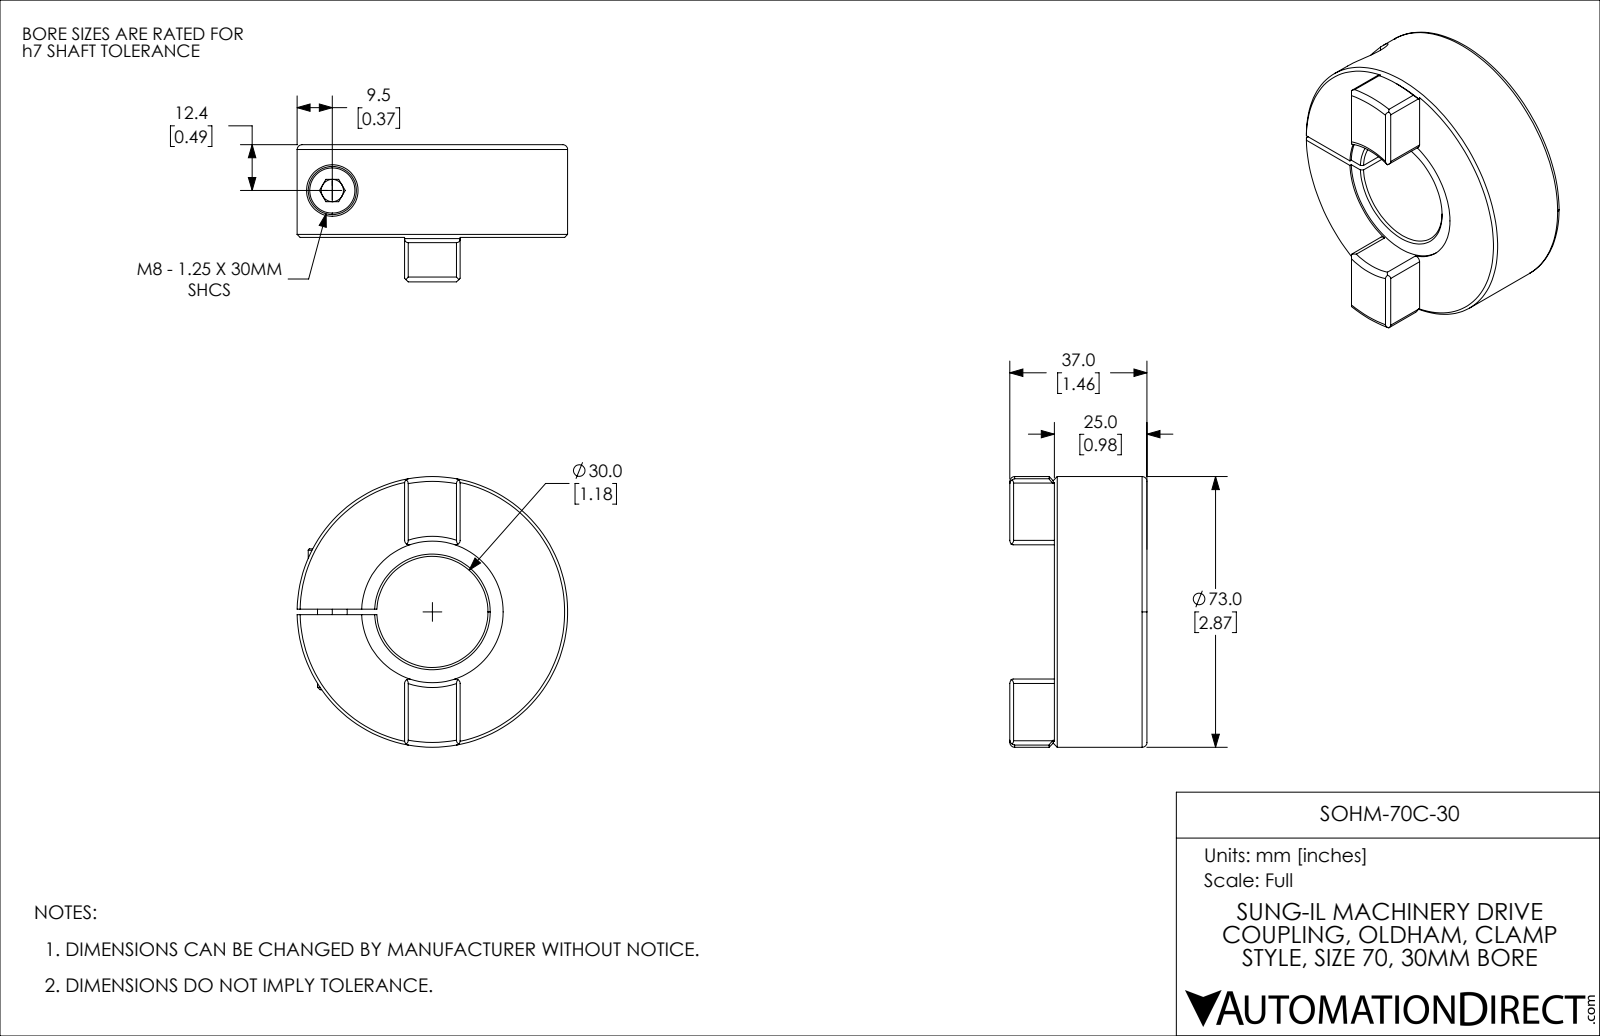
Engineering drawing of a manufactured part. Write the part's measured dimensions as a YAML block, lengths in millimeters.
part_name: "SOHM-70C-30"
step_written_by: "SolidWorks 2021 (CONFIG_CONTROL_DESIGN)"
units: millimeters
bodies: {solids: 2, faces: 90, planar: 35, cylindrical: 30, other: 25}
overall_size: [73, 72.99, 37]
volume: 90678
surface_area: 19754
round_holes:
  - {diameter: 6, count: 1}
  - {diameter: 6.8, count: 1}
  - {diameter: 8.5, count: 1}
  - {diameter: 13.9, count: 1}
  - {diameter: 30, count: 1}
  - {diameter: 38.2, count: 1}
round_bosses_or_shafts:
  - {diameter: 73, count: 1}
  - {diameter: 13, count: 1}
  - {diameter: 8, count: 1}
partial_cylinders:
  - {radius: 1.2, count: 8}
  - {radius: 50, count: 1}
face_to_face_distances: [25, 1.5, 37, 12, 24.5, 0.5, 12.5, 15, 9.75, 8.25]
